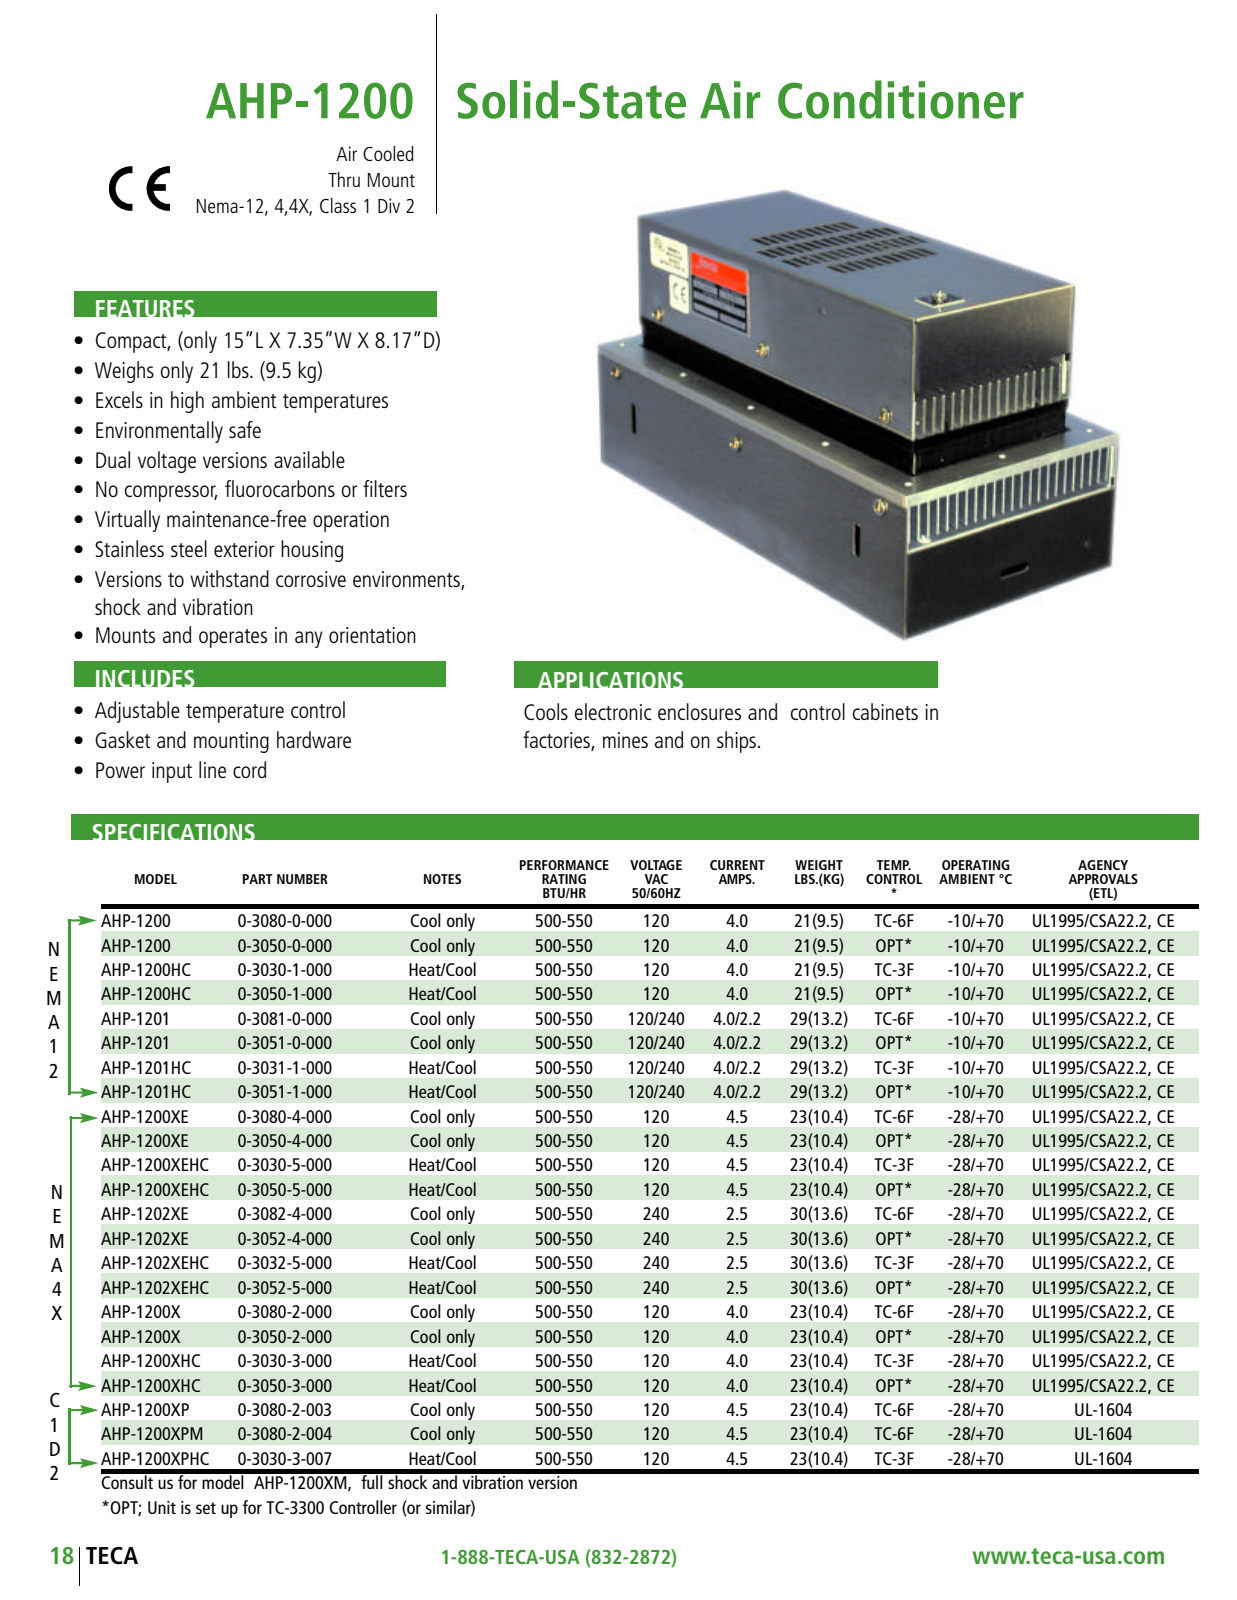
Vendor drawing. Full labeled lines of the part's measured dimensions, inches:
Part name (STEP PRODUCT): ahp-1200
STEP written by: SolidWorks 2019 (CONFIG_CONTROL_DESIGN)
Units: inches
Bodies: 0 solids, 813 faces (702 planar, 107 cylindrical, 4 other)
Overall size (bounding box): 17.353 × 8.372 × 7.346
Round holes (diameter × count): ⌀0.188 ×12, ⌀0.365 ×1, ⌀0.5 ×1, ⌀4.5 ×1, ⌀5.75 ×1
Round bosses / shafts (diameter × count): ⌀3 ×2, ⌀0.527 ×1, ⌀0.475 ×1, ⌀0.414 ×1, ⌀0.38 ×1, ⌀0.25 ×1, ⌀0.15 ×1, ⌀0.125 ×1
Partial cylindrical surfaces — rounded edges, fillets, slot ends (radius × count): R4.072 ×8, R4.74 ×8, R0.125 ×6, R2.8 ×2, R3.25 ×1, R3.375 ×1
Main face-to-face distances: 0.048, 8.122, 7.298, 0.062, 3.73, 3.682, 0.062, 0.924, 6.374, 2.41
Hole centre spacings: 3.452, 7.141, 6.904, 9.313, 6.251, 7.578, 10.356, 10.817
